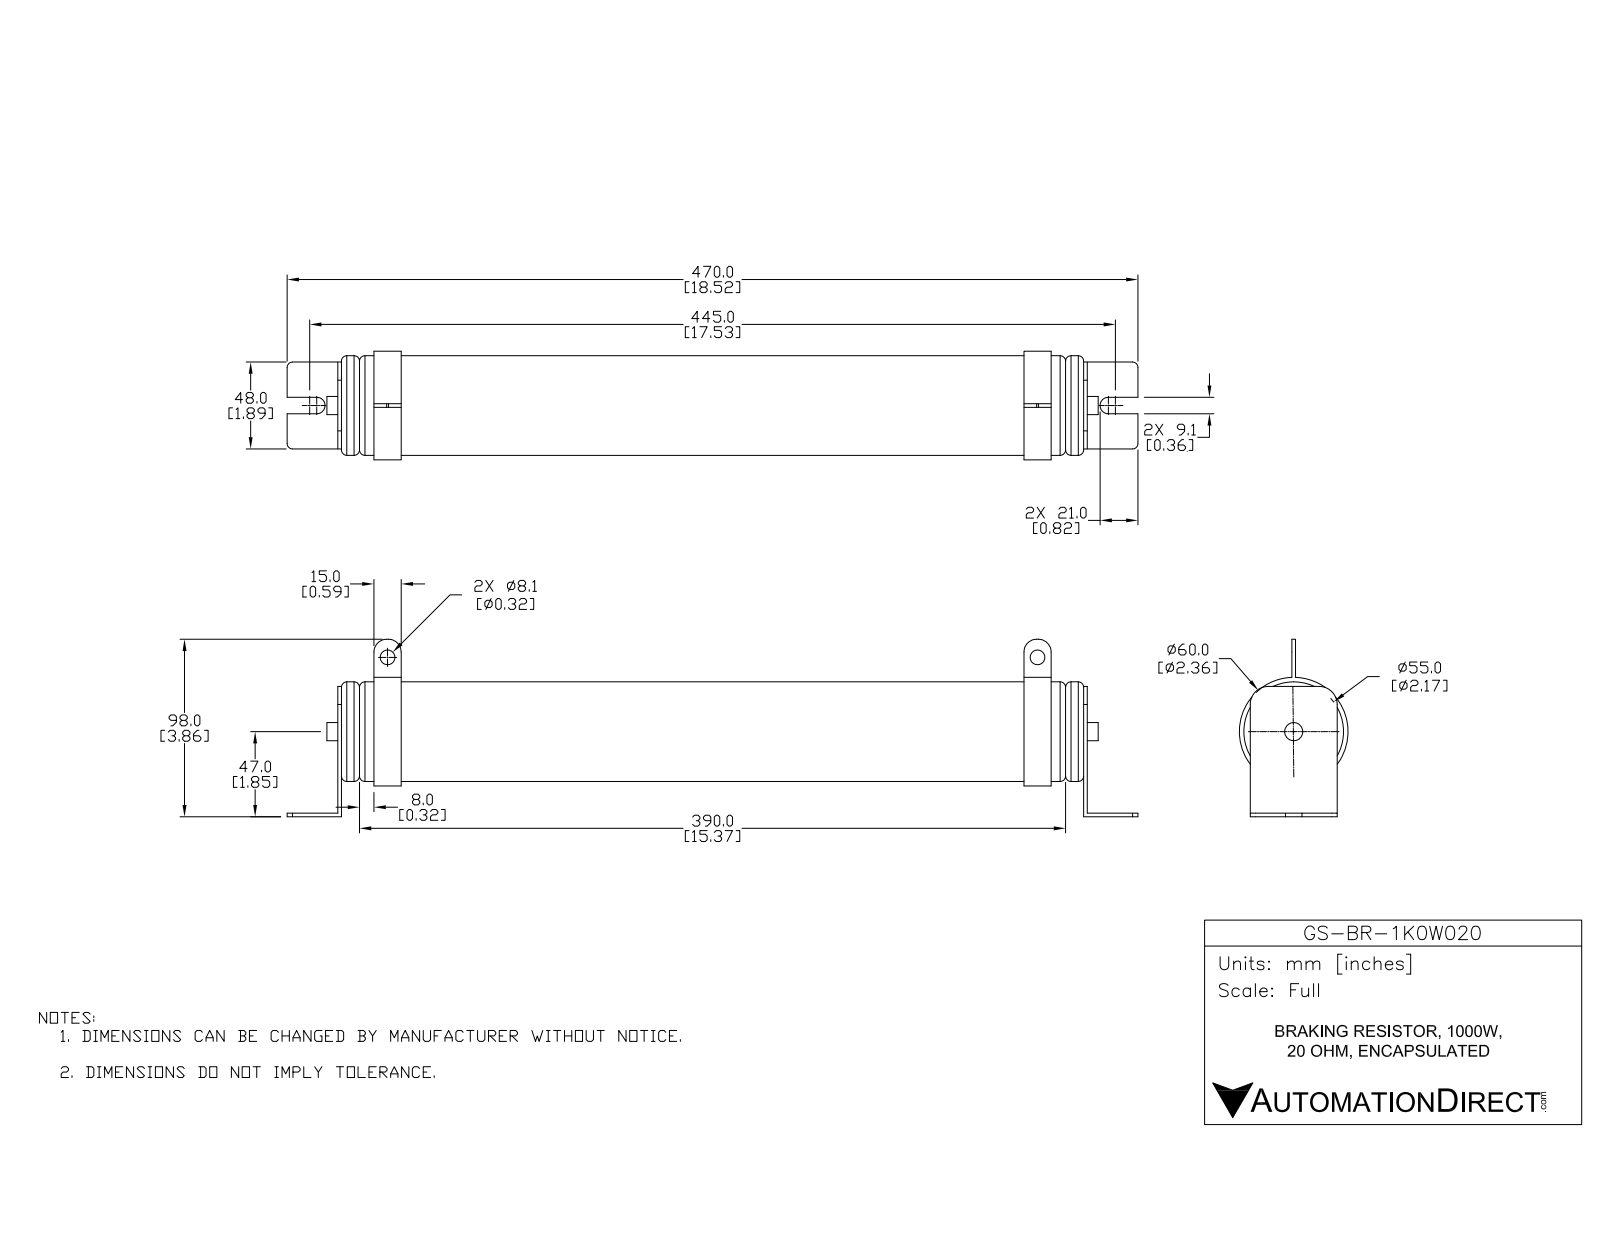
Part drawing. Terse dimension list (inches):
name: GS-BR-1K0W020
written by: SolidWorks 2015 (AUTOMOTIVE_DESIGN)
unit: in
bodies: 2 solids, 91 faces (41 planar, 38 cylindrical, 12 other)
size: 18.504 × 3.858 × 2.362
volume: 61.39 in³; area: 143.2 in²
holes: 2× ⌀0.319
bosses: 1× ⌀2.362, 1× ⌀2.166, 1× ⌀2.165, 1× ⌀0.394
rounds: 4× R0.118, 4× R0.276, 2× R0.179, 2× R0.394
face distances: 0.079, 16.299, 16.22, 16.142, 1.378, 14.921, 1.299, 14.843, 0.787, 15.512
hole spacings: 14.134
